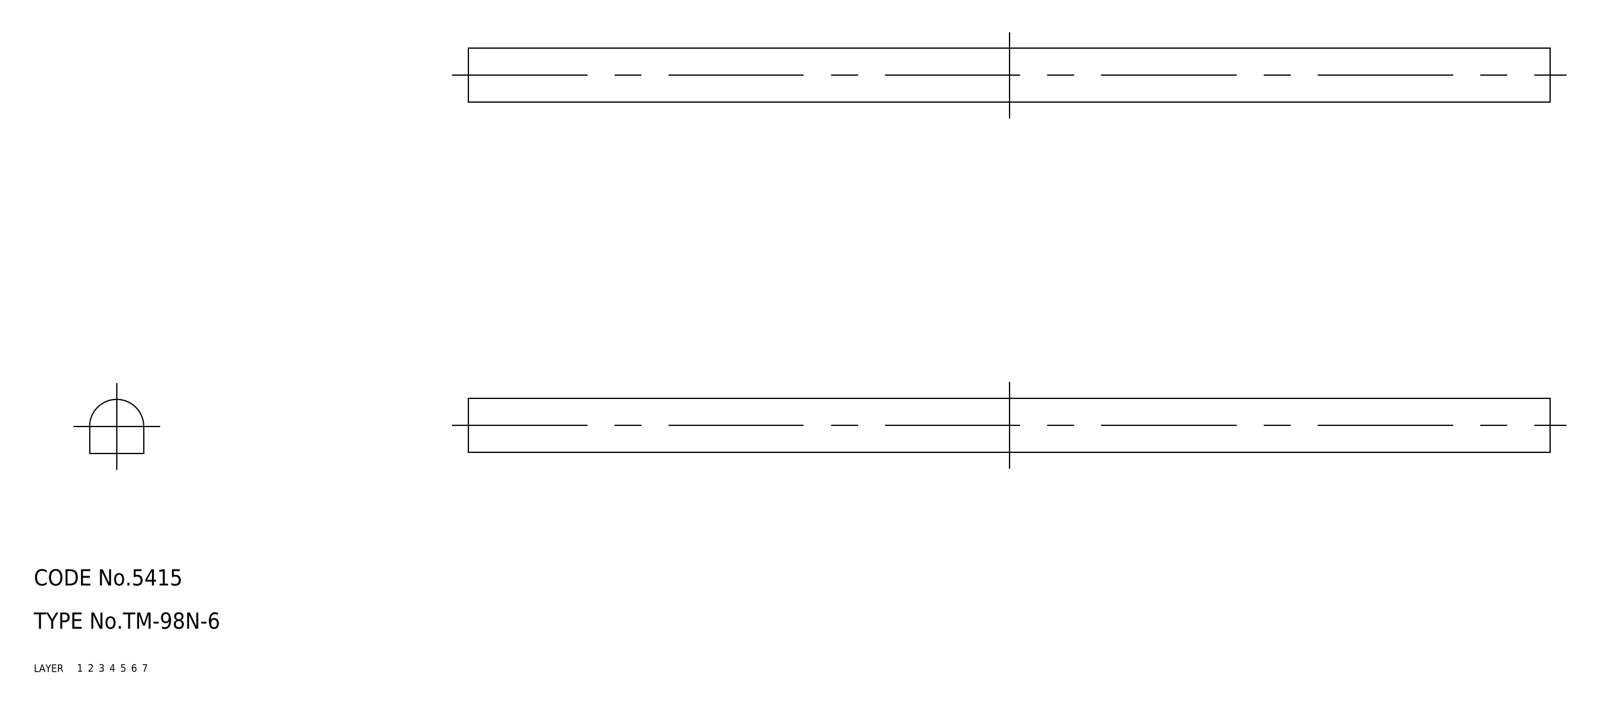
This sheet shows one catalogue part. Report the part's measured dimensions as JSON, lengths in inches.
{"part_name": "rubber foam", "step_written_by": "CADfix (AUTOMOTIVE_DESIGN)", "units": "inches", "bodies": {"solids": 1, "faces": 6, "planar": 0, "cylindrical": 0, "other": 6}, "overall_size": [7.874, 0.394, 0.394], "volume_in3": 1.09, "surface_area_in2": 11.35}
